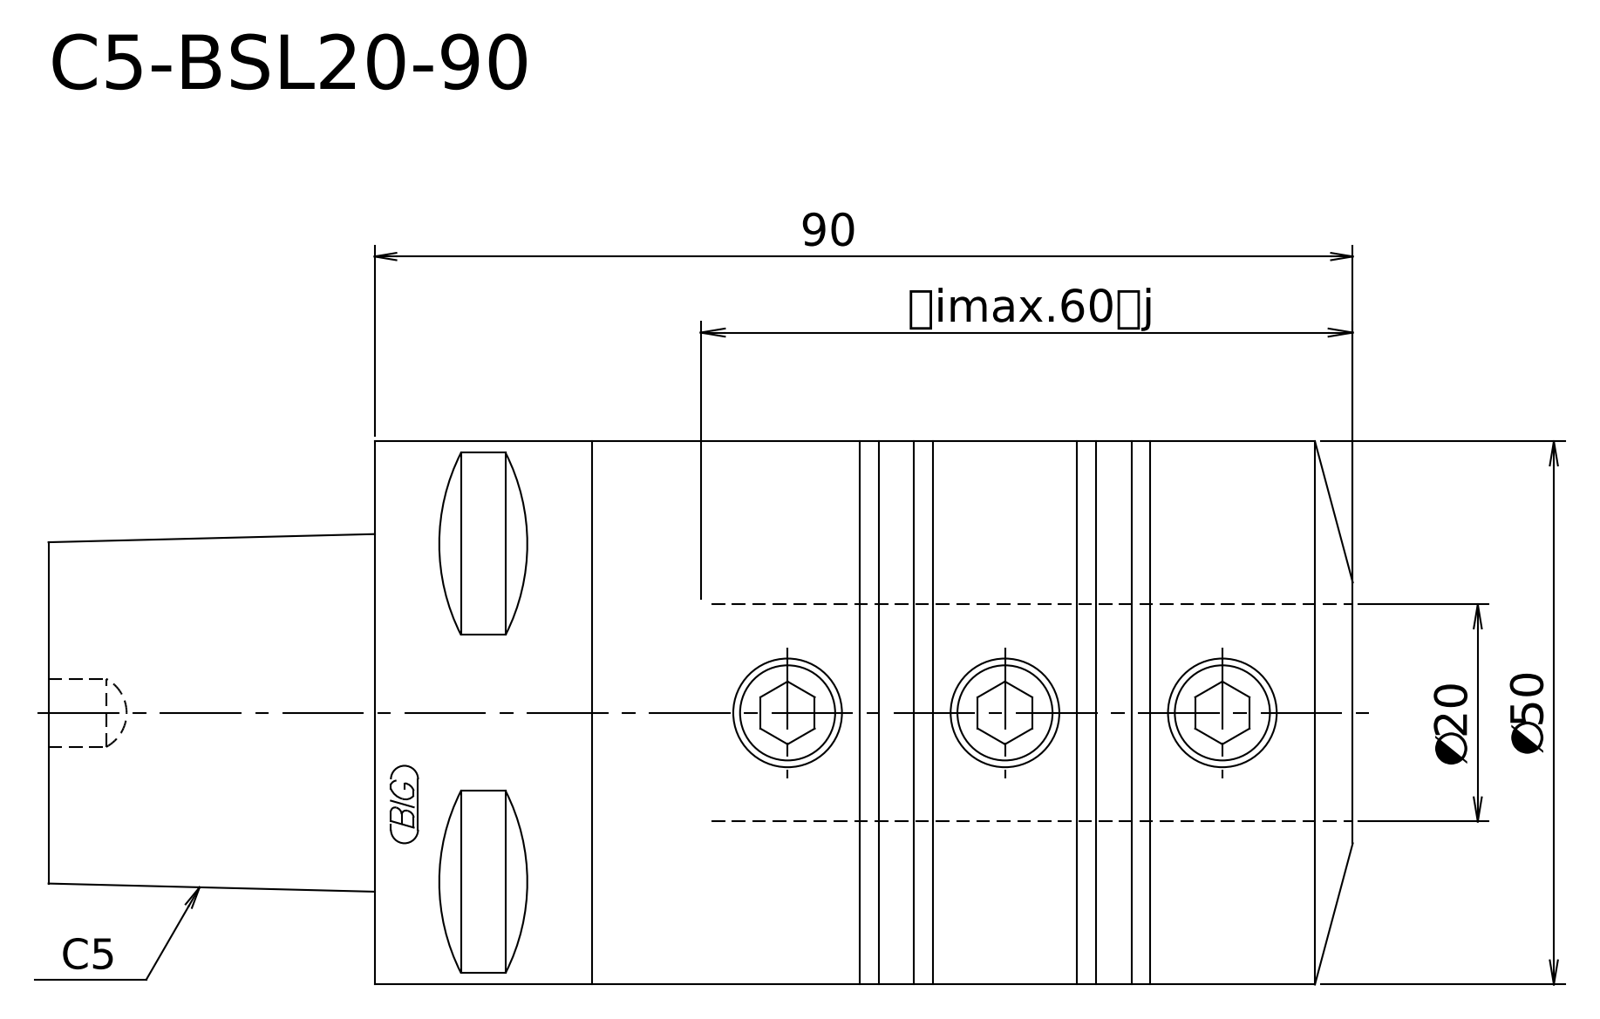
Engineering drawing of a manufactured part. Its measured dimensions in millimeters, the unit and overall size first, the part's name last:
Units: millimetres
Overall size (bounding box): 120 × 49.98 × 49.98
Round bosses / shafts (diameter × count): ⌀49.98 ×1
Main face-to-face distances: 30, 90, 120
Volume: 200 870 mm³ · Surface area: 20 724 mm²
Bodies: 1 solid, 6 faces (3 planar, 1 cylindrical, 2 other)
STEP written by: Kubotek KeyCreator V8.5.1 (14335) (CONFIG_CONTROL_DESIGN)
